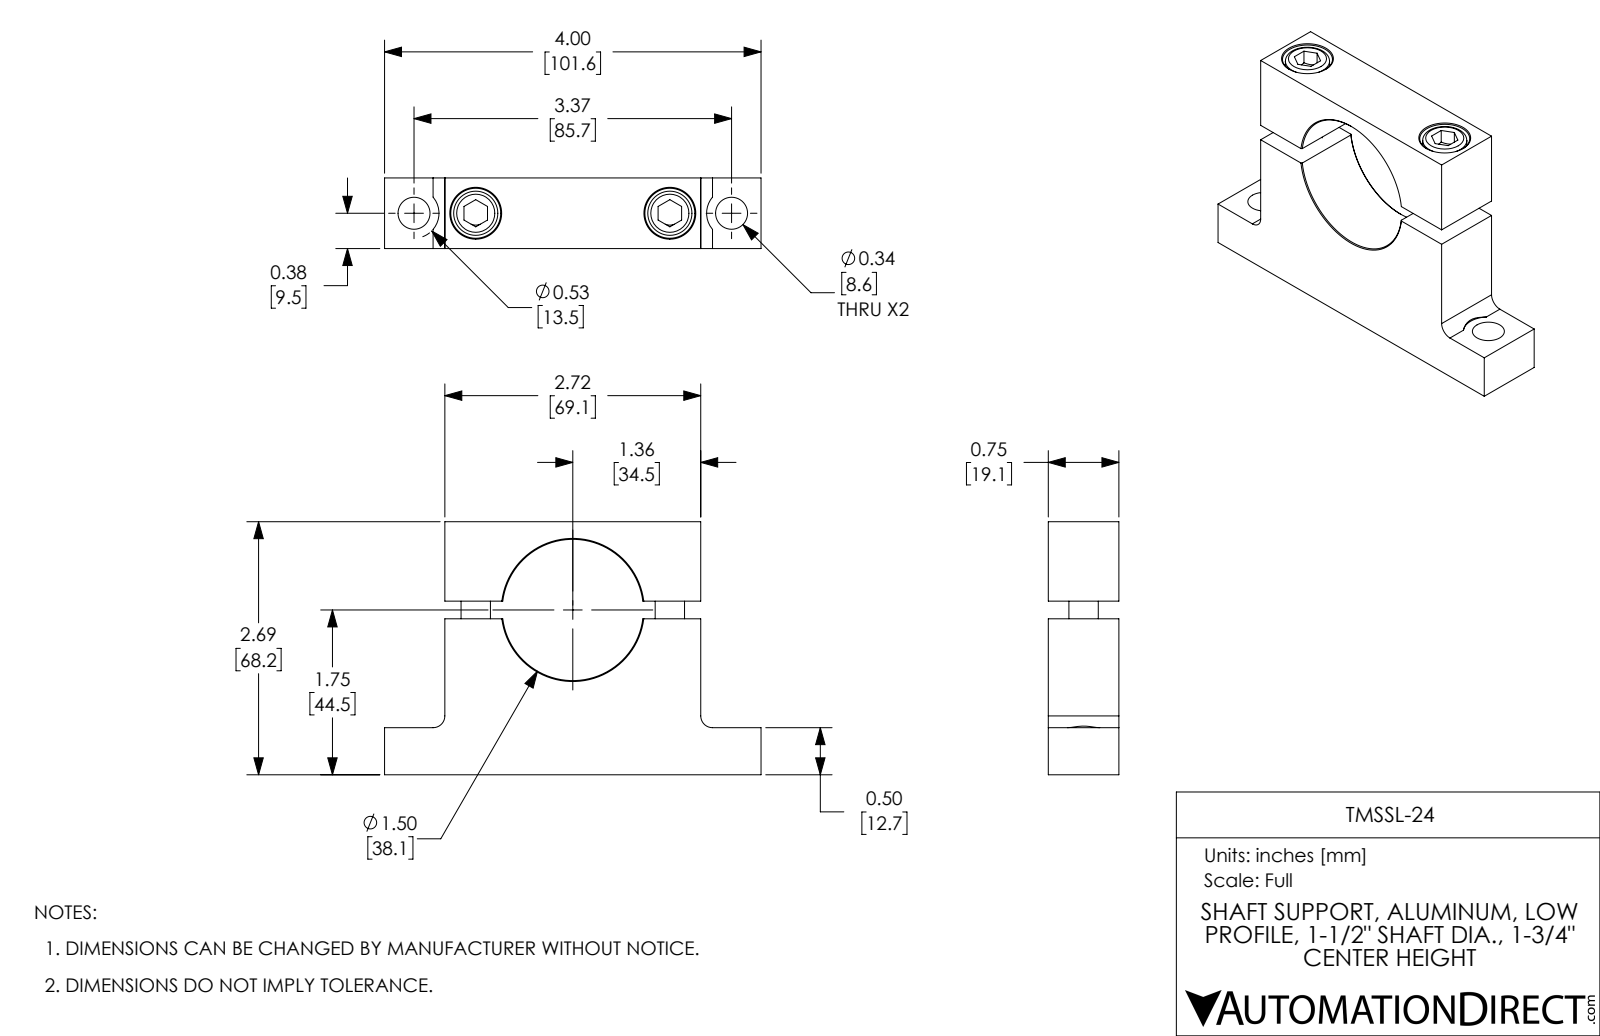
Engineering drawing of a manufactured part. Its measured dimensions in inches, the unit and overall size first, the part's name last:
Units: inches
Overall size (bounding box): 4 × 2.687 × 0.75
Round holes (diameter × count): ⌀0.252 ×2, ⌀0.332 ×2, ⌀0.34 ×2, ⌀0.531 ×2, ⌀1.5 ×1
Round bosses / shafts (diameter × count): ⌀0.469 ×2, ⌀0.312 ×2
Partial cylindrical surfaces — rounded edges, fillets, slot ends (radius × count): R0.125 ×2, R0.266 ×2
Main face-to-face distances: 0.75, 2.687, 2.719, 1.656, 1.031, 0.641, 3.359, 1.844, 0.187, 0.843
Hole centre spacings: 0.656, 2.718, 2.062, 3.374
Volume: 4.258 in³ · Surface area: 35.81 in²
Bodies: 4 solids, 92 faces (38 planar, 30 cylindrical, 24 other)
Part name (STEP PRODUCT): TMSSL-24
STEP written by: SolidWorks 2017 (AUTOMOTIVE_DESIGN)
